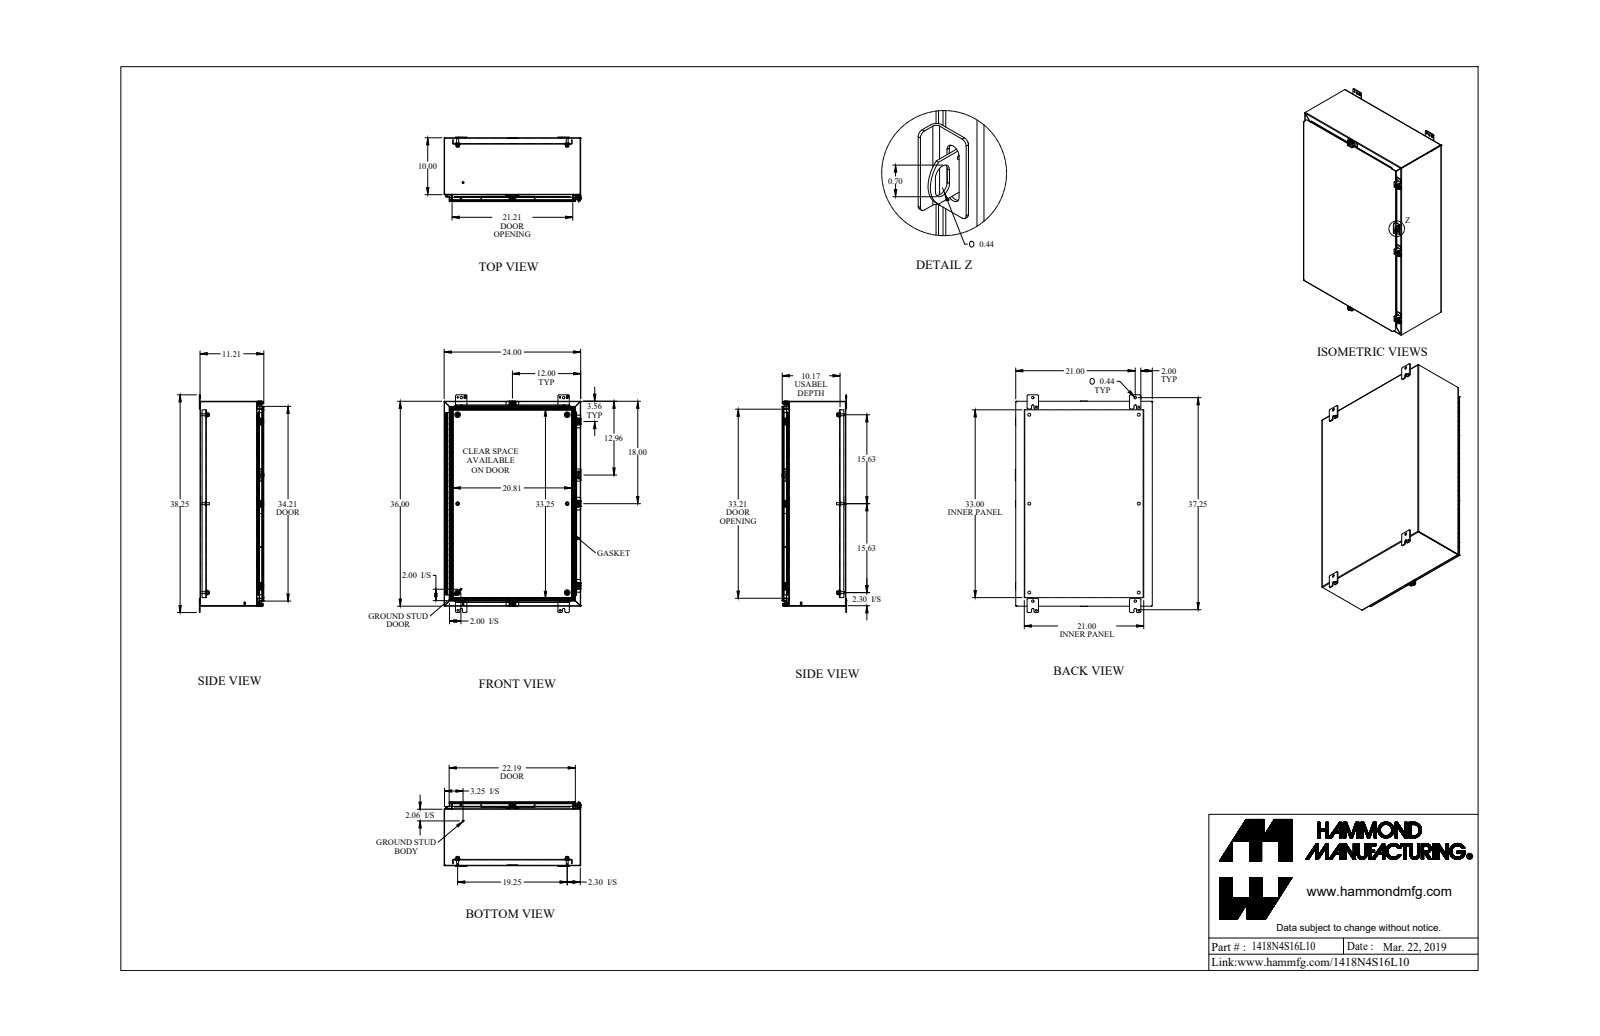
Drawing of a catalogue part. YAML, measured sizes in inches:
part_name: "1418N4S16L10_Default"
step_written_by: "SolidWorks 2019 (CONFIG_CONTROL_DESIGN)"
units: inches
bodies: {solids: 50, faces: 1665, planar: 878, cylindrical: 633, other: 154}
overall_size: [38.25, 24.063, 11.375]
volume: 319.7
surface_area: 8400
round_holes:
  - {diameter: 0.5, count: 6}
  - {diameter: 0.213, count: 5}
  - {diameter: 0.265, count: 5}
  - {diameter: 0.375, count: 5}
  - {diameter: 0.307, count: 4}
  - {diameter: 0.313, count: 4}
  - {diameter: 0.437, count: 4}
  - {diameter: 0.445, count: 4}
  - {diameter: 0.11, count: 1}
  - {diameter: 0.125, count: 1}
round_bosses_or_shafts:
  - {diameter: 0.65, count: 6}
  - {diameter: 0.375, count: 6}
  - {diameter: 0.332, count: 6}
  - {diameter: 0.5, count: 5}
  - {diameter: 0.39, count: 5}
  - {diameter: 0.244, count: 5}
  - {diameter: 1, count: 4}
  - {diameter: 0.313, count: 2}
partial_cylinders:
  - {radius: 0.048, count: 27}
  - {radius: 0.143, count: 27}
  - {radius: 0.188, count: 26}
  - {radius: 0.036, count: 24}
  - {radius: 0.108, count: 24}
  - {radius: 0.25, count: 24}
  - {radius: 0.125, count: 12}
  - {radius: 0.141, count: 10}
face_to_face_distances: [0.072, 11.066, 11.138, 0.072, 11.138, 0.937, 11.21, 0.095, 1.009, 23.928]
hole_center_spacings: [15.625, 34.735, 19.25, 24.793, 31.25, 9.857, 36.703, 9.857]
